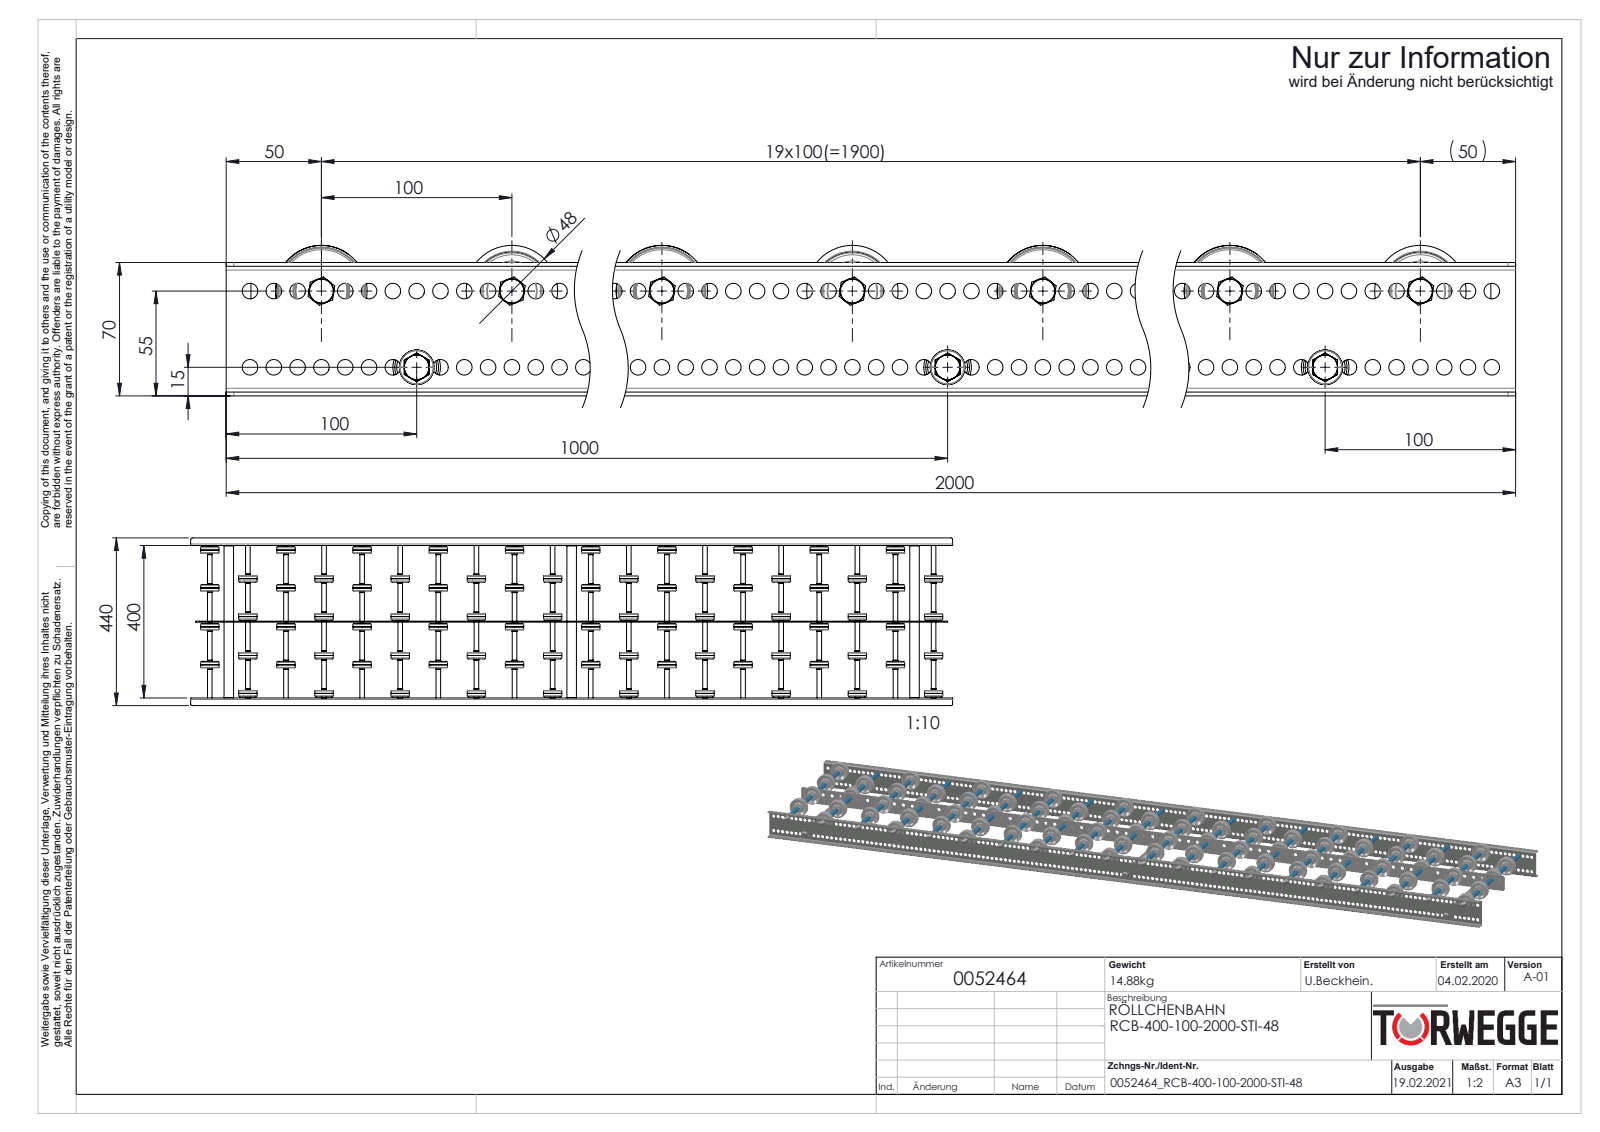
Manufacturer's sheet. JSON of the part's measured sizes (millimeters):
{"part_name": "S100994_Sperrzahnschraube_M08x16-8.8-A2K; K0011528_2200-48-8; 0046278_KB-ROHR-12X1,75mm_KFG_L75,5; S106837_Gewindestange-M8-KFG_L420 (+6 more)", "step_written_by": "SolidWorks 2020 (AUTOMOTIVE_DESIGN)", "units": "millimeters", "bodies": {"solids": 318, "faces": 9994, "planar": 1968, "cylindrical": 4110, "other": 3916}, "overall_size": [2000, 440, 79], "volume_mm3": 3555000, "surface_area_mm2": 2821000, "round_holes": [[8.2, 318], [8.5, 79], [6.65, 20], [8, 20], [9.65, 20], [15, 20], [41, 20], [6.8, 3], [21, 3]], "round_bosses_or_shafts": [[48, 20], [13, 20], [12.5, 20], [12.4, 20], [12, 20], [11.5, 20], [25, 3], [8, 3]], "partial_cylinders_radius": [[4, 8], [2, 4], [5, 4]], "face_to_face_distances": [2, 201.5, 402, 201, 99.5, 75, 68, 404, 400, 186.5], "hole_center_spacings": [12.5, 25, 37.5, 50, 62.5, 75, 87.5, 100]}
